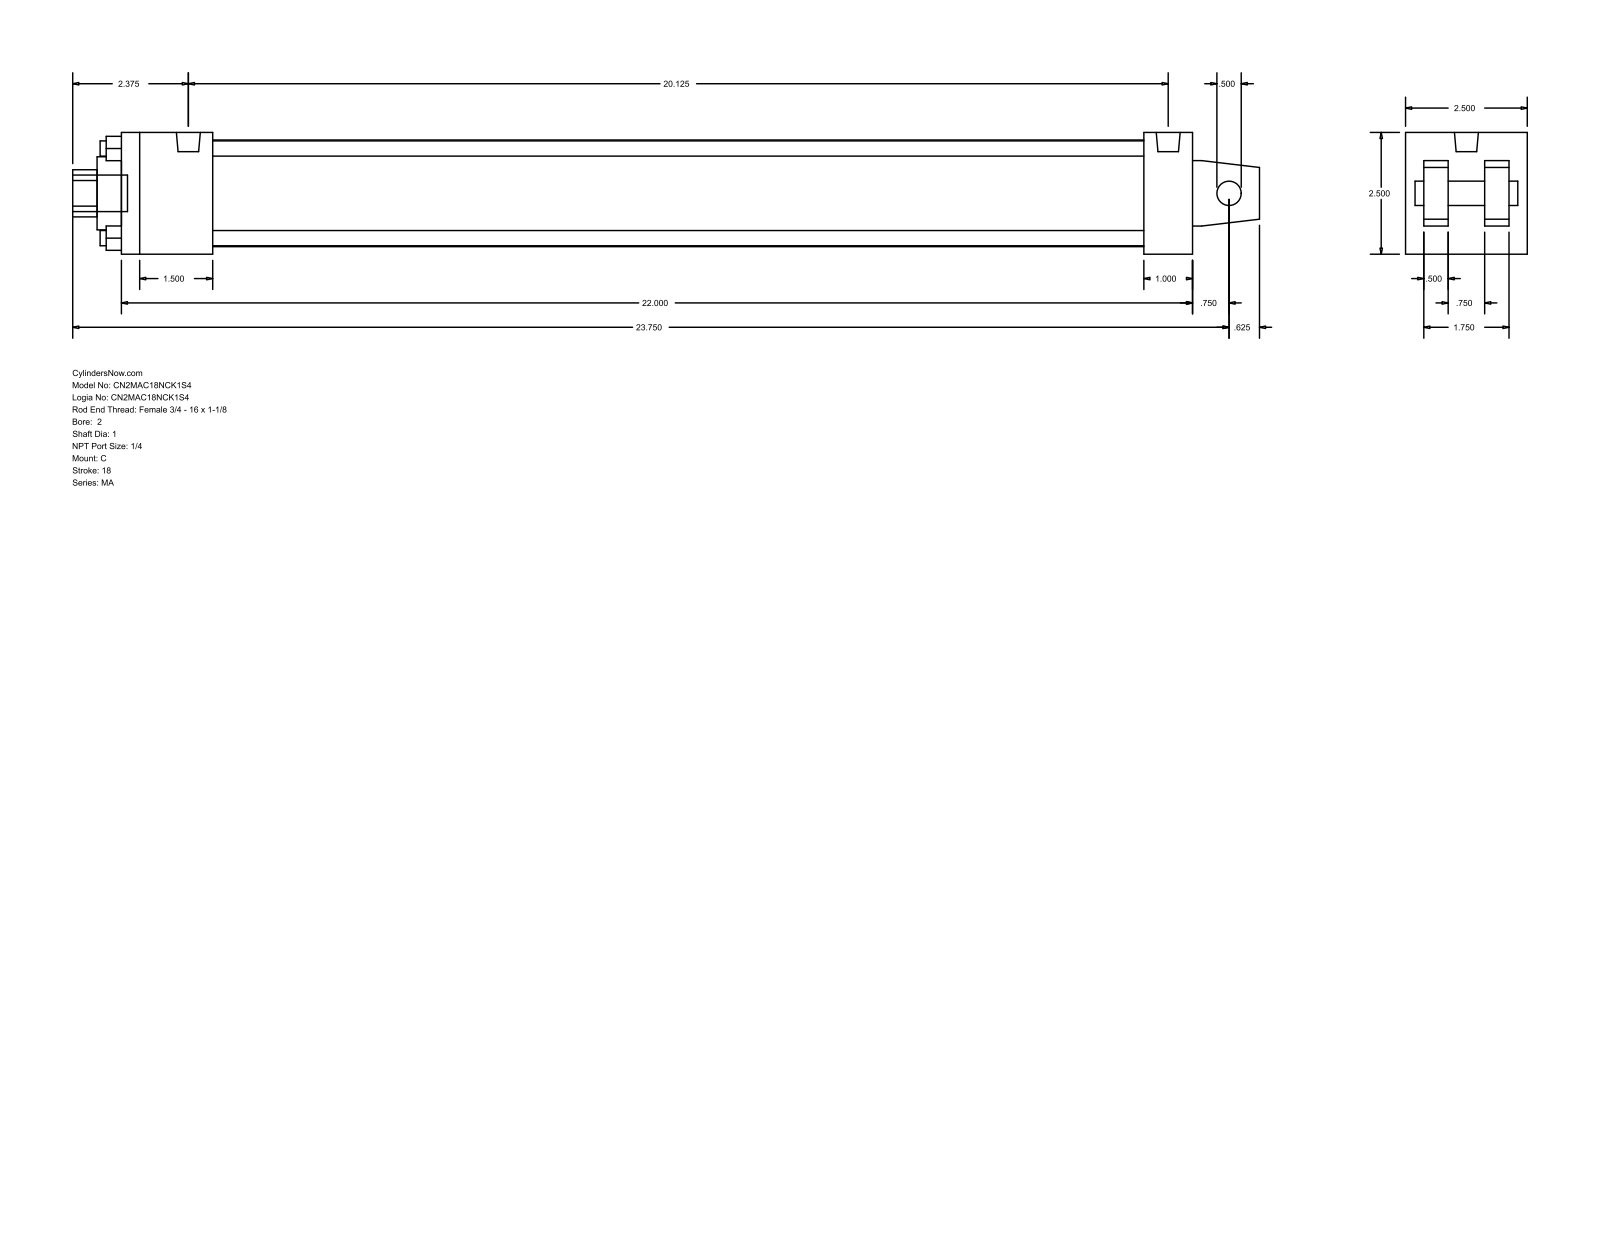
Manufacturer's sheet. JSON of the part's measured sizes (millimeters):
{"part_name": "MA_C__0200_1", "step_written_by": "GSSL Pune (CONFIG_CONTROL_DESIGN)", "units": "millimeters", "bodies": {"solids": 0, "faces": 103, "planar": 76, "cylindrical": 27, "other": 0}, "overall_size": [619.12, 63.5, 63.5], "round_holes": [[7.94, 4], [12.7, 1], [25.4, 1], [38.1, 1], [55.63, 1]], "round_bosses_or_shafts": [[7.94, 4], [12.49, 2], [19.05, 1]], "partial_cylinders_radius": [[12.29, 1]], "face_to_face_distances": [63.5, 12.7, 558.8, 22.22, 41.28, 9.52, 53.98, 31.76, 47.63, 25.4], "hole_center_spacings": [33.05, 46.74, 66.1]}
